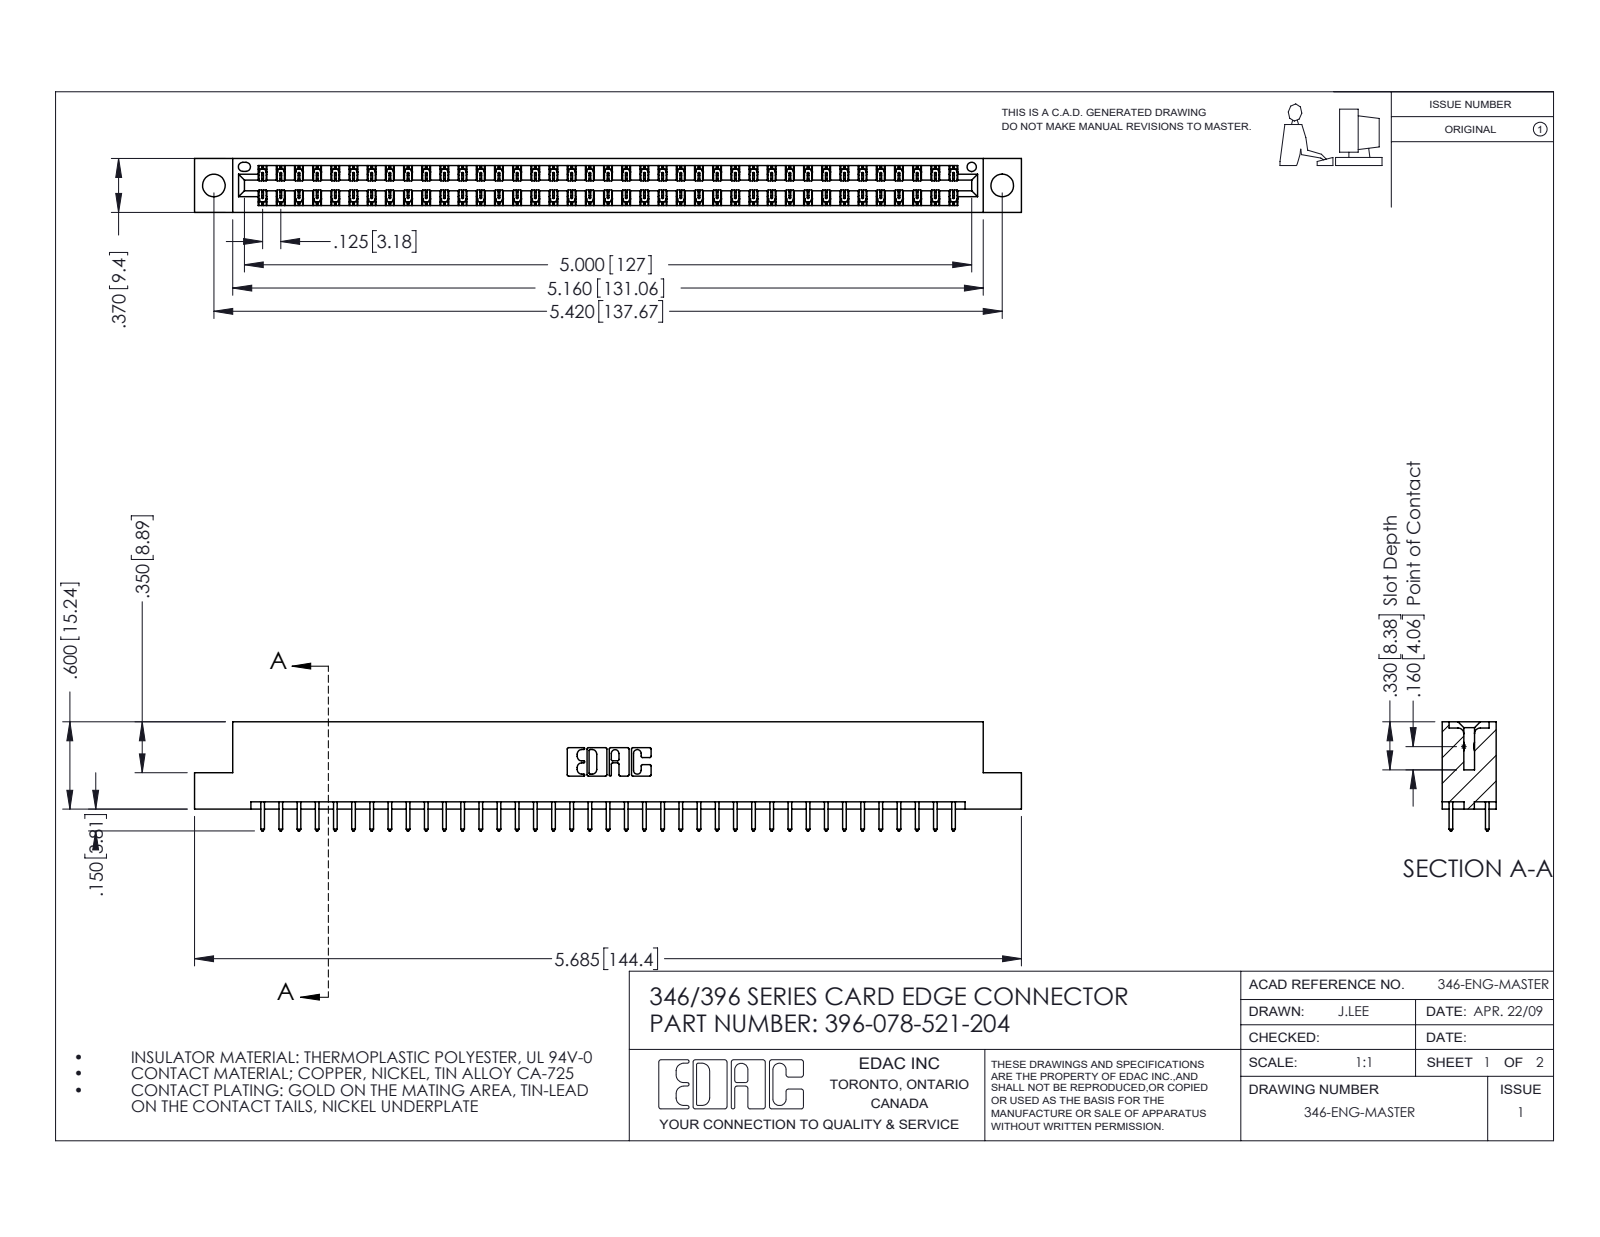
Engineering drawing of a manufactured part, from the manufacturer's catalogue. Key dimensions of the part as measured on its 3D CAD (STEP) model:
Part name (STEP PRODUCT): 346 Part_Flush Mounting Lugs - 0.156 Dia-TH; 345-292-001_345-293-121; 396-078-521-204
STEP written by: SolidWorks 2016 (CONFIG_CONTROL_DESIGN)
Units: inches
Bodies: 79 solids, 4178 faces (2806 planar, 1372 cylindrical, 0 other)
Overall size (bounding box): 5.685 × 0.75 × 0.37
Volume: 0.851 in³ · Surface area: 29 in²
Round holes (diameter × count): ⌀0.156 ×2, ⌀0.064 ×1
Partial cylindrical surfaces — rounded edges, fillets, slot ends (radius × count): R0.006 ×117, R0.01 ×78, R0.01 ×22, R0.007 ×6, R0.031 ×6, R0.026 ×3, R0.014 ×2, R0.022 ×2
Main face-to-face distances: 0.048, 0.322, 0.25, 0.37, 0.072, 0.298, 0.025, 0.275, 0.148, 0.222
Hole centre spacings: 0.246, 5.211, 5.42
